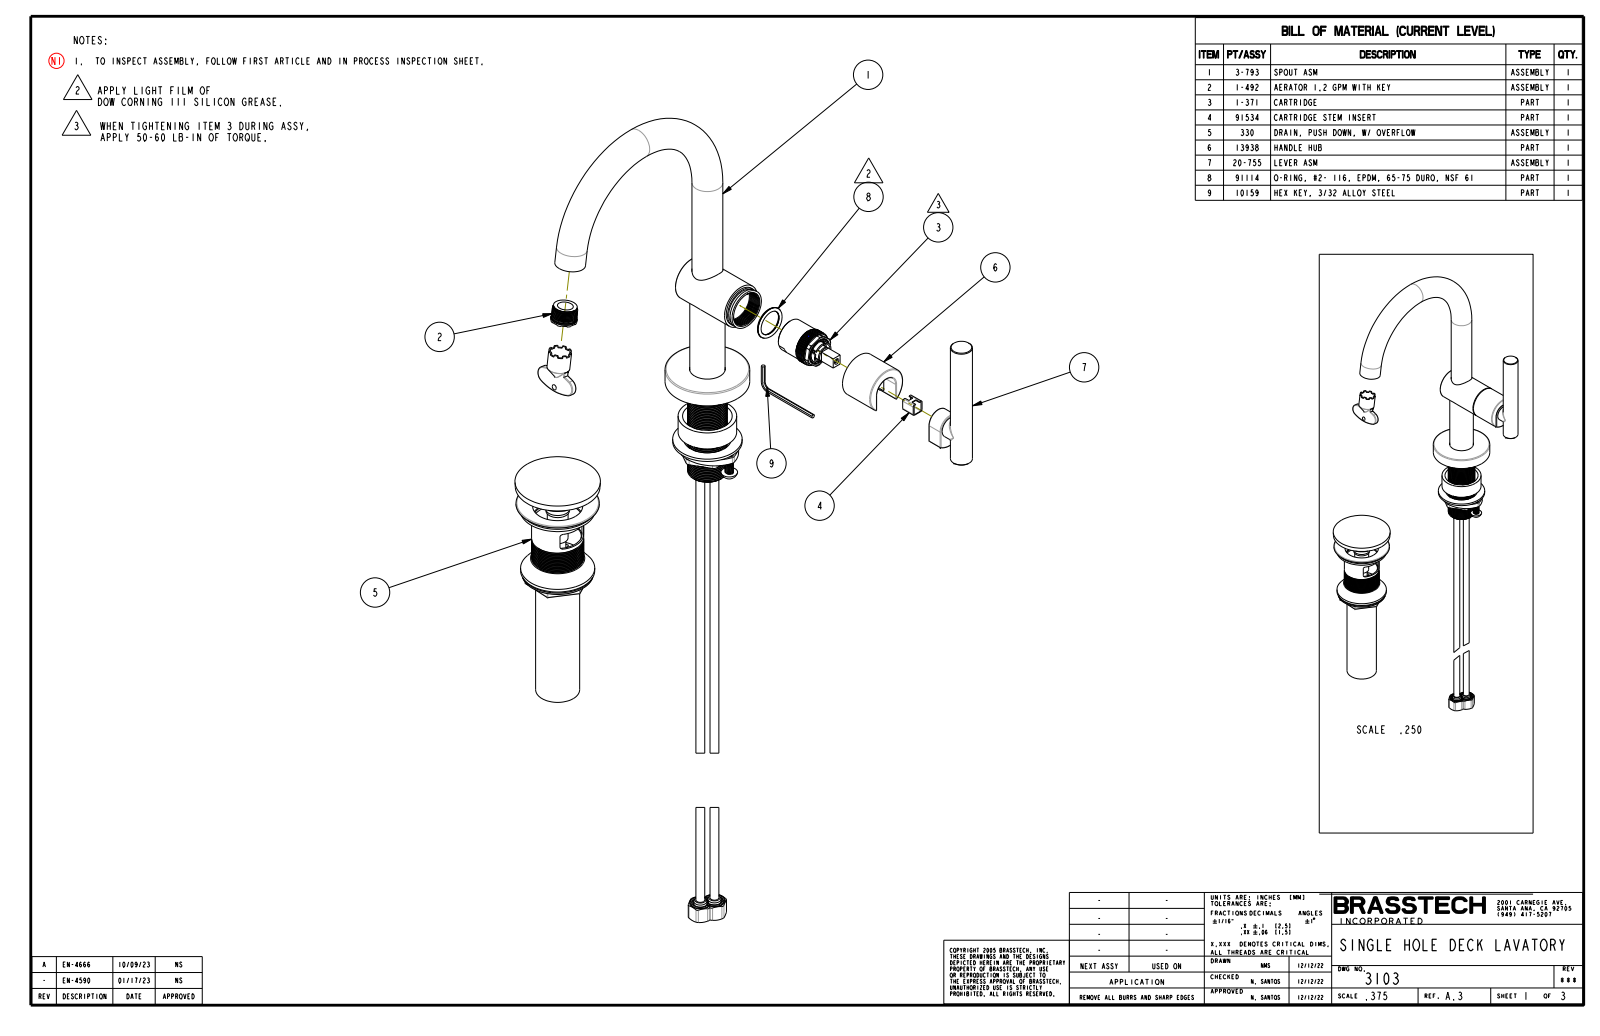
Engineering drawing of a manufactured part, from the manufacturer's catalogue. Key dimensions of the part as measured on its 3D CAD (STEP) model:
Part name (STEP PRODUCT): 11764; 11884; 2-741_ASM; 13847 (+8 more)
STEP written by: CREO PARAMETRIC BY PTC INC, 2023134 (CONFIG_CONTROL_DESIGN)
Units: inches
Bodies: 17 solids, 1297 faces (321 planar, 539 cylindrical, 437 other)
Overall size (bounding box): 10.529 × 7.133 × 4.464
Volume: 8.646 in³ · Surface area: 228.5 in²
Round holes (diameter × count): ⌀0.156 ×5, ⌀0.222 ×3, ⌀0.303 ×3, ⌀0.13 ×2, ⌀0.158 ×2, ⌀0.25 ×2, ⌀0.375 ×2, ⌀0.777 ×2, ⌀0.13 ×1, ⌀0.157 ×1, ⌀0.16 ×1, ⌀0.175 ×1
Round bosses / shafts (diameter × count): ⌀0.875 ×2, ⌀0.625 ×2, ⌀0.152 ×2, ⌀2.4 ×1, ⌀2 ×1, ⌀1.313 ×1, ⌀1.3 ×1, ⌀1.175 ×1
Partial cylindrical surfaces — rounded edges, fillets, slot ends (radius × count): R0.02 ×10, R0.01 ×8, R0.06 ×8, R0.1 ×8, R0.02 ×6, R0.04 ×6, R0.01 ×4, R0.015 ×4
Main face-to-face distances: 0.438, 0.08, 3.117, 2.642, 0.475, 0.358, 0.014, 1.913, 1.19, 1.452
Hole centre spacings: 0.216, 0.207, 0.287, 0.3, 0.362, 0.365, 0.365, 0.374
